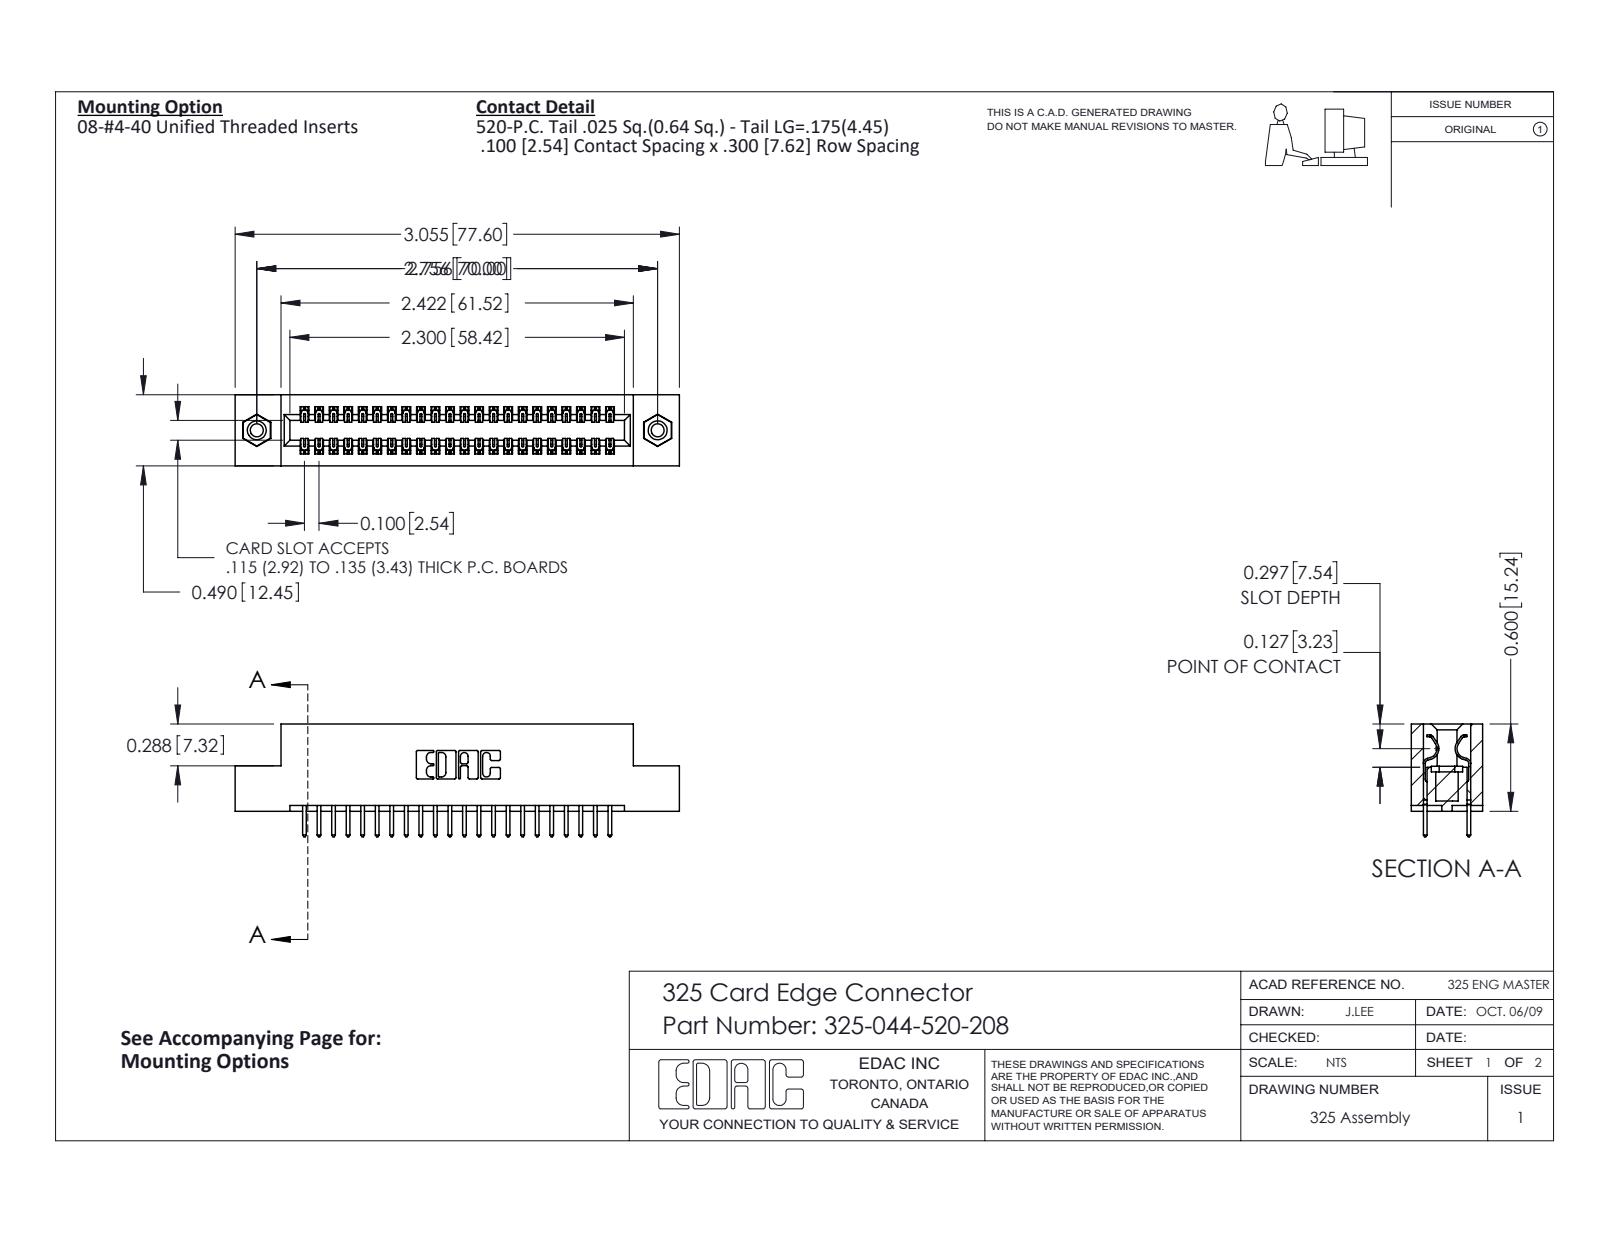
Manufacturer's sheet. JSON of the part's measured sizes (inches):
{"part_name": "345-250-001_345-250-003-102; 325-292-001_325-293-120; 325 Part_TI; 325-044-520-208", "step_written_by": "SolidWorks 2016 (CONFIG_CONTROL_DESIGN)", "units": "inches", "bodies": {"solids": 47, "faces": 2462, "planar": 1686, "cylindrical": 760, "other": 16}, "overall_size": [3.055, 0.775, 0.49], "volume_in3": 0.6, "surface_area_in2": 17.58, "round_holes": [[0.089, 2], [0.125, 2], [0.16, 2]], "round_bosses_or_shafts": [[0.155, 2]], "partial_cylinders_radius": [[0.006, 66], [0.01, 44], [0.01, 22], [0.007, 6], [0.031, 6], [0.026, 3], [0.014, 2], [0.022, 2]], "face_to_face_distances": [0.083, 0.407, 0.3, 0.49, 0.107, 0.383, 0.025, 0.325, 0.04, 0.1], "hole_center_spacings": [2.756]}
